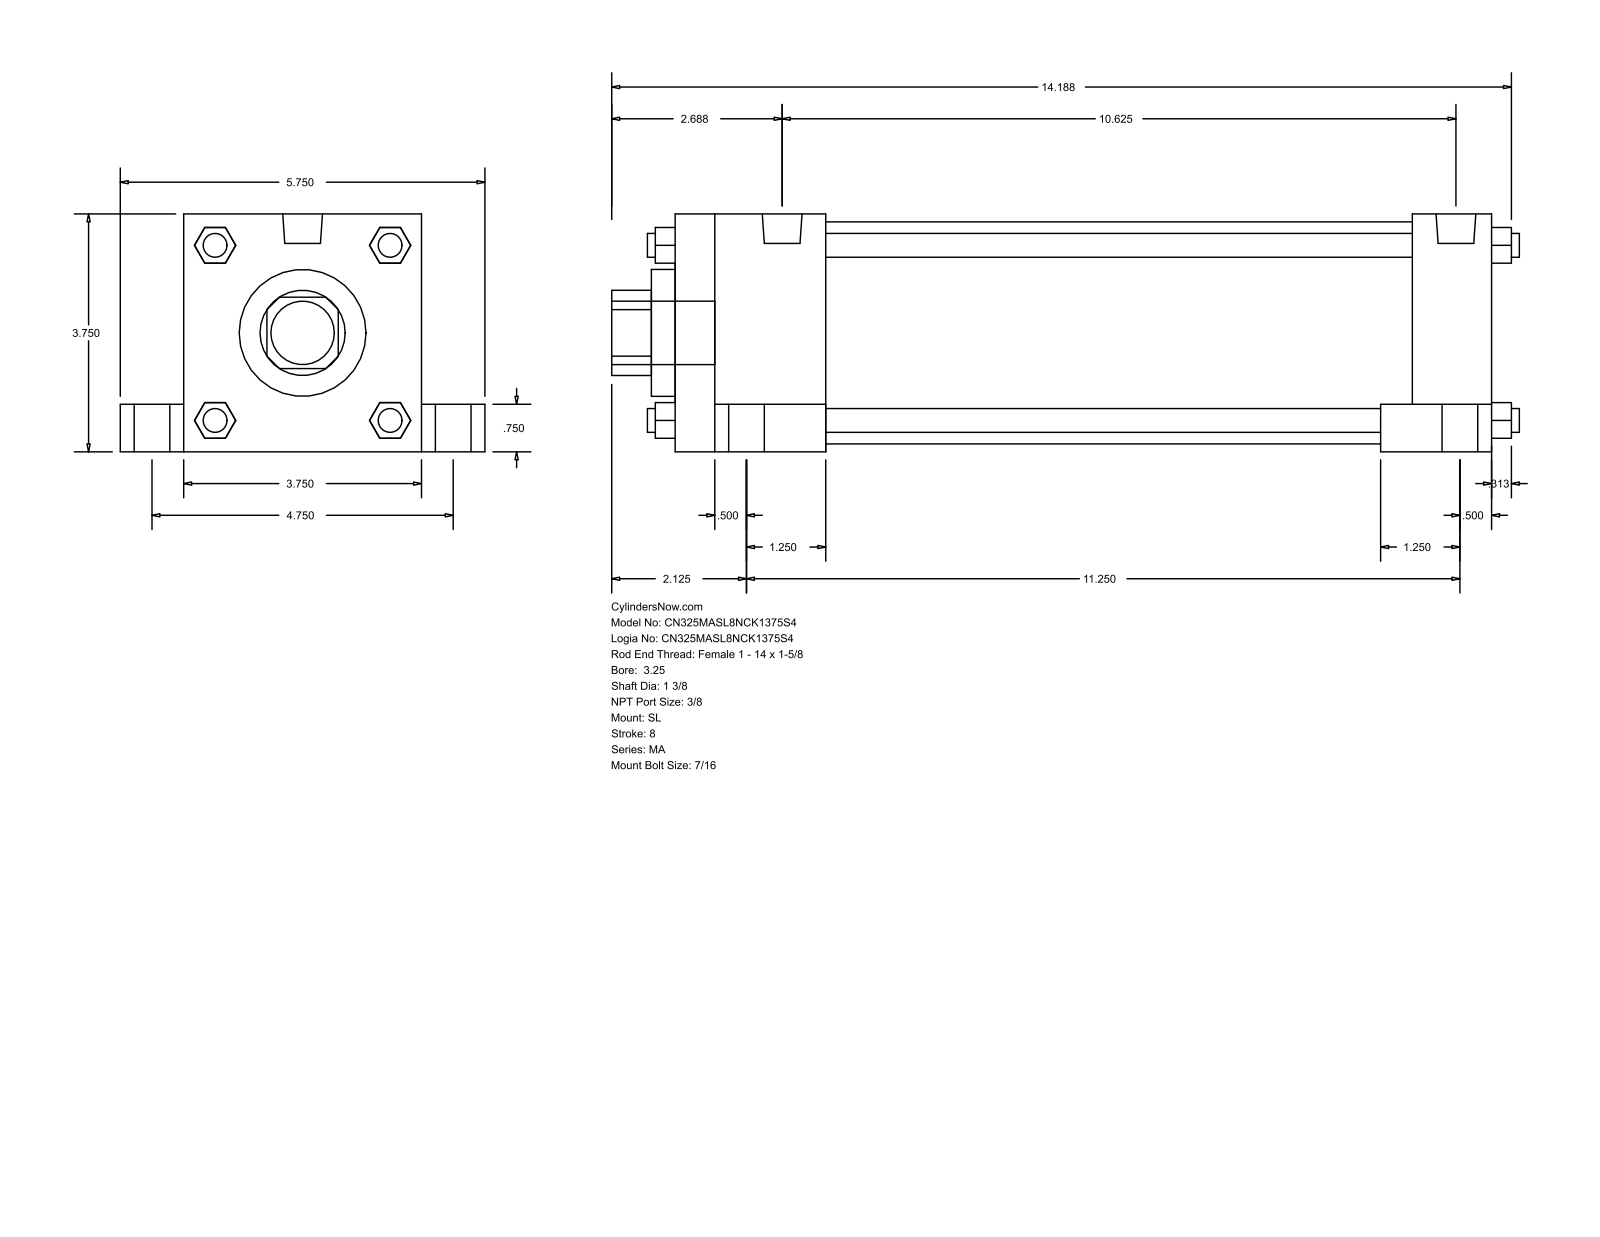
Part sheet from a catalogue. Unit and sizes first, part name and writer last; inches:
Units: inches
Overall size (bounding box): 14.313 × 5.75 × 3.75
Round holes (diameter × count): ⌀1.375 ×1, ⌀2 ×1, ⌀3.5 ×1
Round bosses / shafts (diameter × count): ⌀0.813 ×4, ⌀0.563 ×4, ⌀0.437 ×4, ⌀0.375 ×4, ⌀0.627 ×2, ⌀1 ×1
Partial cylindrical surfaces — rounded edges, fillets, slot ends (radius × count): R0.672 ×1
Main face-to-face distances: 3.75, 12.875, 1, 4.75, 11.625, 1.25, 2.375, 9.25, 10.5, 0.75
Bodies: 0 solids, 148 faces (112 planar, 36 cylindrical, 0 other)
Part name (STEP PRODUCT): MA_SL__0325_1.375
STEP written by: GSSL Pune (CONFIG_CONTROL_DESIGN)
